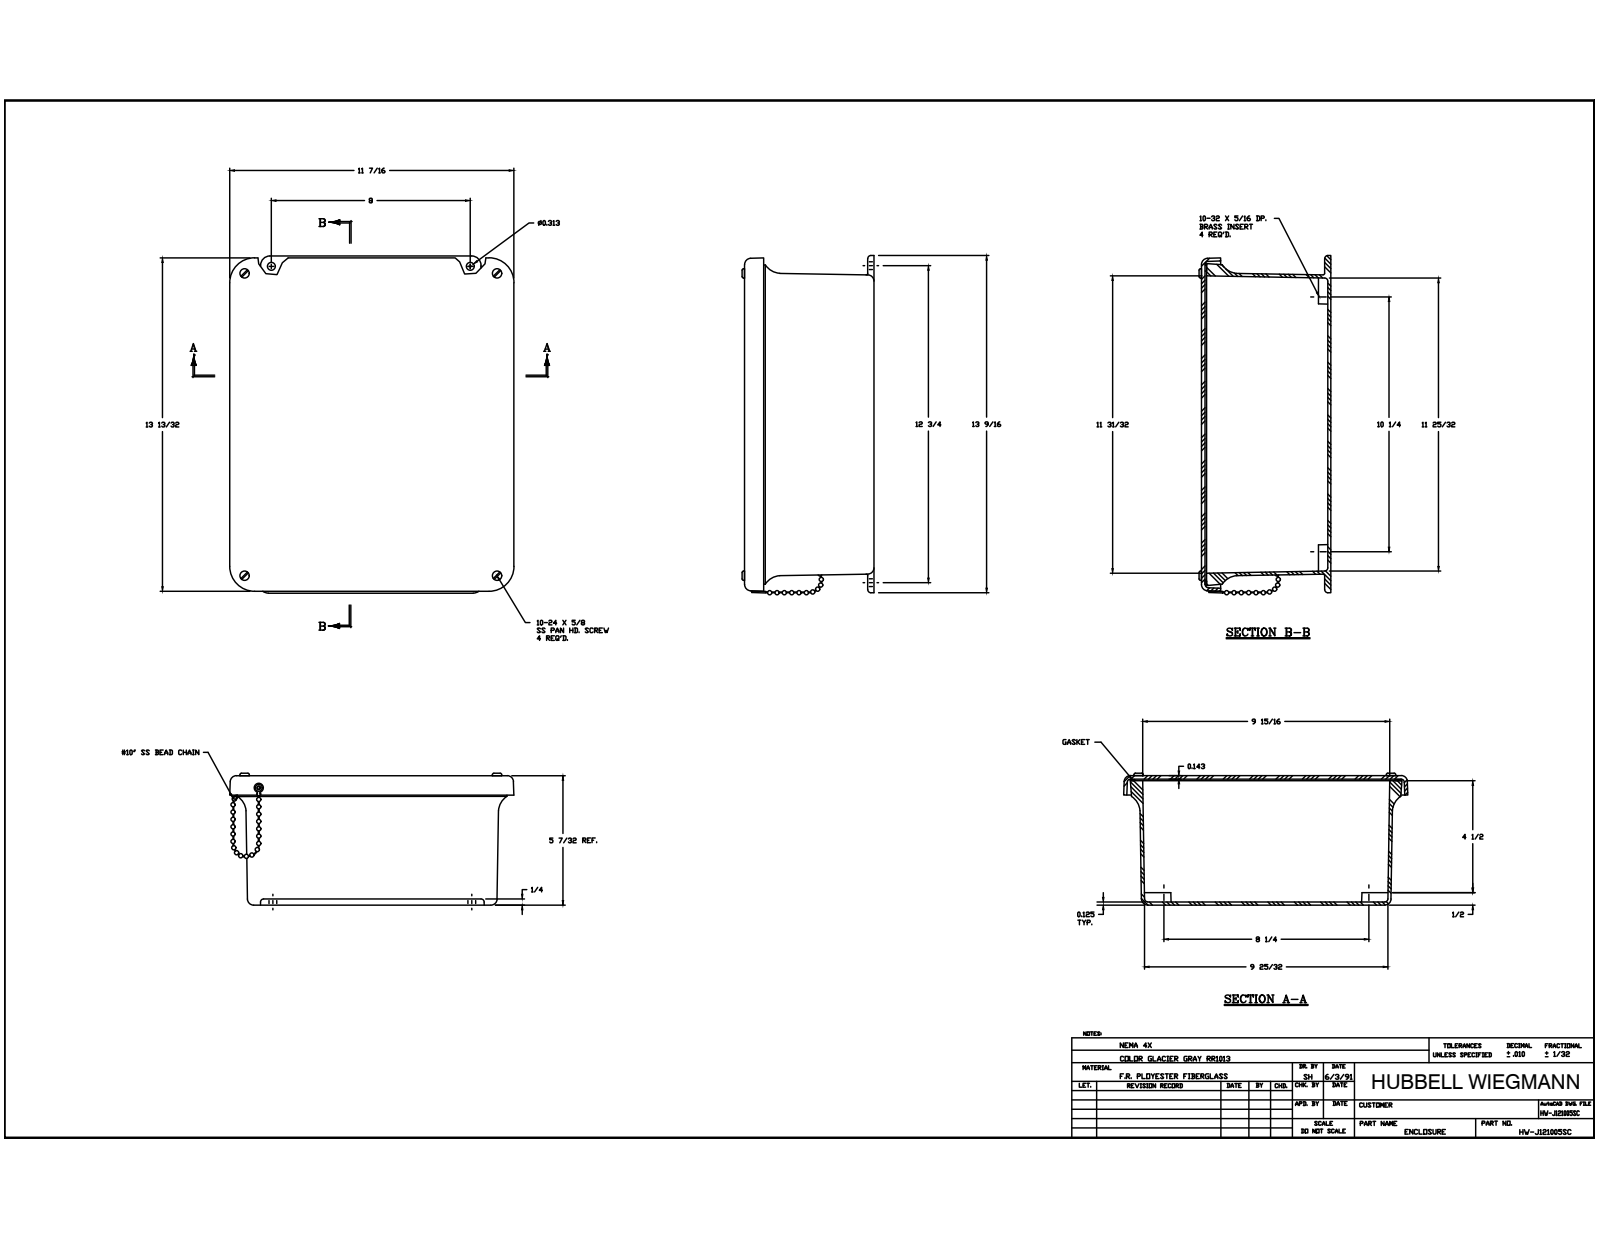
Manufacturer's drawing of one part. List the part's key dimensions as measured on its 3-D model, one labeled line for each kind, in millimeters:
Part name (STEP PRODUCT): J1210W_1; RMINS45821P_119; RMINS45821P_120; RMINS45821P_121 (+8 more)
STEP written by: Autodesk Inventor 2014 (AUTOMOTIVE_DESIGN)
Units: millimetres
Bodies: 21 solids, 862 faces (187 planar, 287 cylindrical, 388 other)
Overall size (bounding box): 358.7 × 298.44 × 135.89
Volume: 1 412 000 mm³ · Surface area: 733 638 mm²
Round holes (diameter × count): ⌀3.56 ×5, ⌀3.86 ×5, ⌀3.68 ×4, ⌀3.96 ×4, ⌀5.54 ×4, ⌀4.76 ×2, ⌀3.2 ×1
Round bosses / shafts (diameter × count): ⌀6.86 ×8, ⌀4.83 ×4, ⌀3.97 ×4, ⌀9.52 ×2, ⌀6.35 ×2, ⌀3.17 ×2, ⌀7.19 ×1
Partial cylindrical surfaces — rounded edges, fillets, slot ends (radius × count): R0.79 ×20, R3.17 ×14, R5.08 ×8, R6.35 ×8, R9.53 ×4, R19.05 ×4, R0.25 ×2, R1.6 ×2
Main face-to-face distances: 3.63, 3.18, 128.93, 132.56, 125.75, 129.38, 123.82, 5.56, 127, 1.93
Hole centre spacings: 368.26, 34.23, 92.08, 174.62, 209.55, 235, 235.01, 257.96
